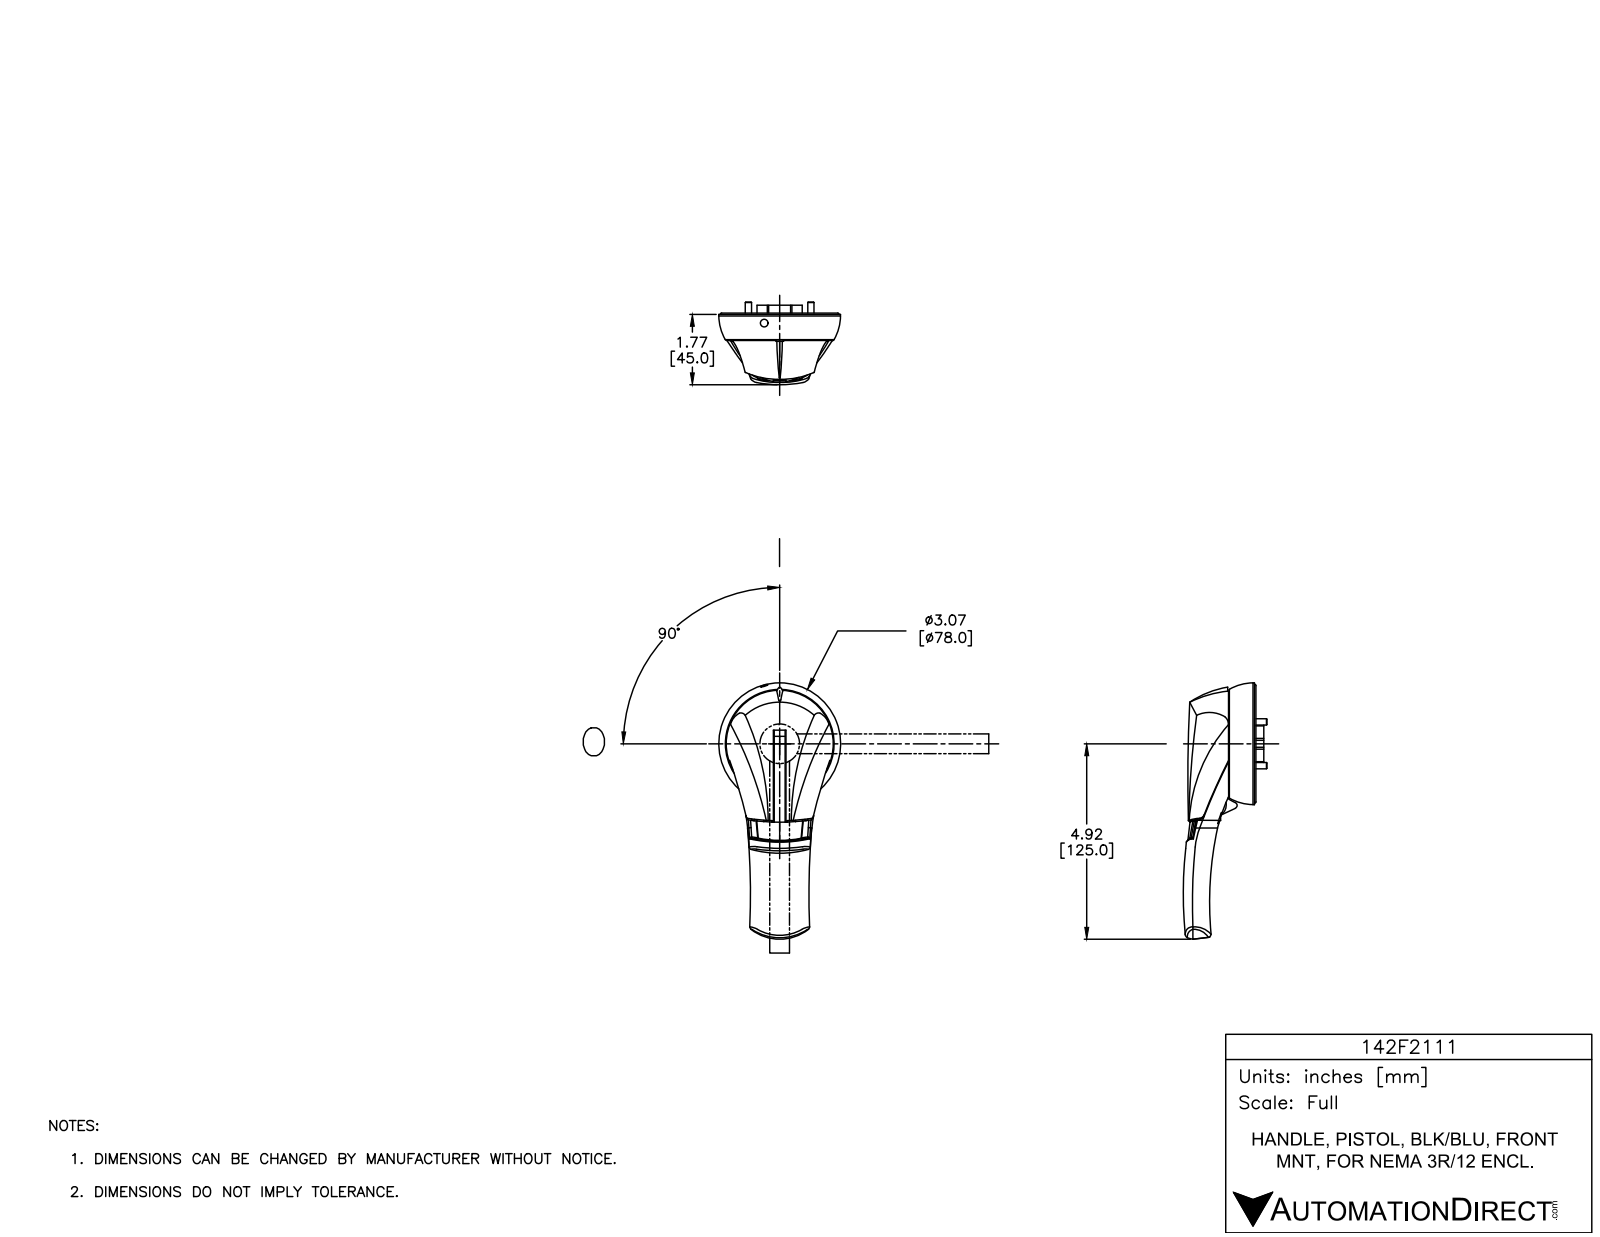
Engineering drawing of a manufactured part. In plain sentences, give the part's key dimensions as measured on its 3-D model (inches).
The part is named "142F2111". Its 3-D file was written by "SolidWorks 2015 (AUTOMOTIVE_DESIGN)". It is 8 solids with 1516 faces: 810 planar, 548 cylindrical and 158 other. Overall it measures 6.458 by 3.07 by 2.079 inches. Its volume is 9.514 cubic inches and its surface area 87.32 square inches. Round holes: 6 of diameter 0.157, 4 of diameter 0.339, 4 of diameter 0.425, 3 of diameter 0.03, 2 of diameter 0.169, 2 of diameter 0.362, 1 of diameter 0.118, 1 of diameter 0.189, 1 of diameter 2.992. Round bosses or shafts: 11 of diameter 0.02, 4 of diameter 0.335, 4 of diameter 0.315, 3 of diameter 0.089, 3 of diameter 0.069, 2 of diameter 0.228, 1 of diameter 2.819, 1 of diameter 2.701. Partial cylindrical surfaces (rounded edges, fillets, slot ends): 221 of radius 0.01, 20 of radius 0.015, 20 of radius 0.034, 15 of radius 0.03, 4 of radius 0.039, 3 of radius 0.025, 3 of radius 5.437, 2 of radius 0.079. The main face-to-face distances are 0.024, 0.701, 0.713, 0.689, 0.035, 0.102, 0.276, 0.173, 0.244, 0.047. The hole center spacings are 0.961, 0.309, 0.669, 1.098, 1.102, 1.203, 1.575, 1.881.
